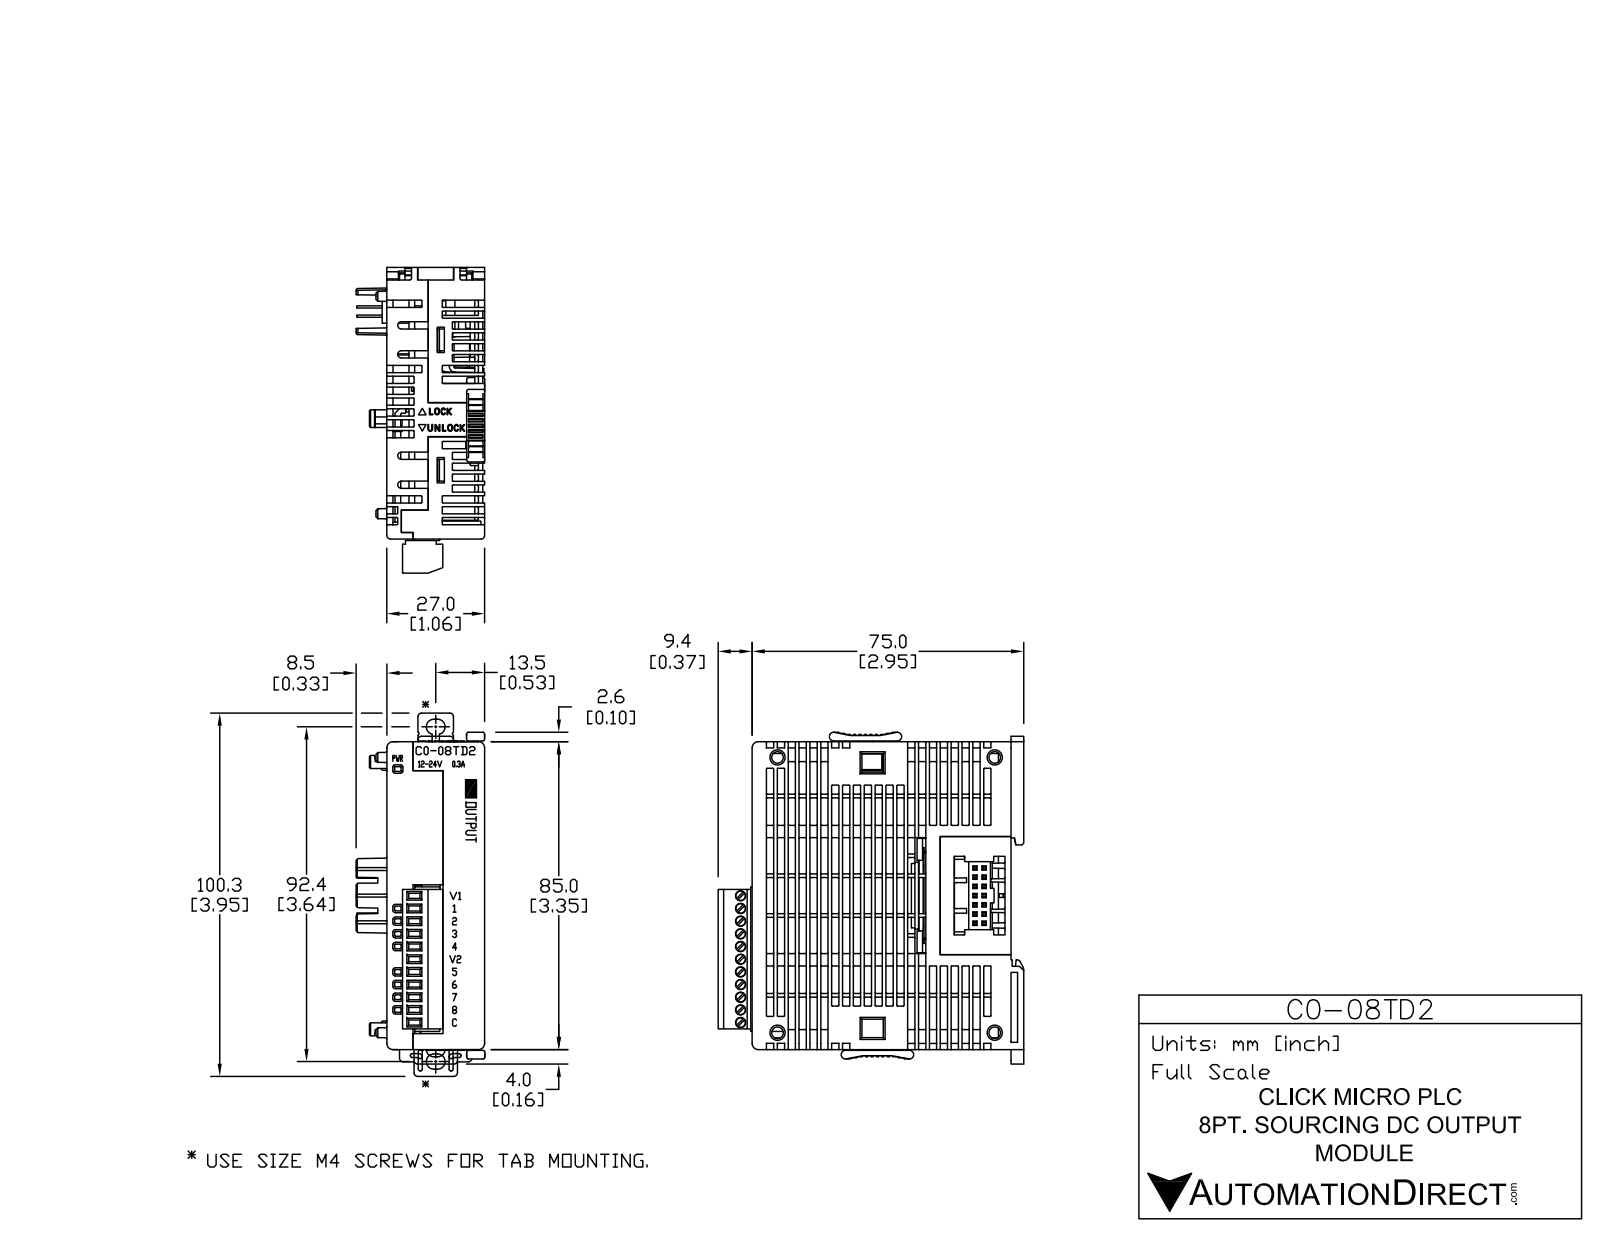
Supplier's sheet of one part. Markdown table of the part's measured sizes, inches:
| quantity | value |
| --- | --- |
| part name | C0-08TD2 |
| STEP written by | SolidWorks 2009 (AUTOMOTIVE_DESIGN) |
| units | inches |
| bodies | 1 solid, 3689 faces (2637 planar, 968 cylindrical, 84 other) |
| overall size | 3.606 × 3.323 × 1.4 |
| volume | 9.917 in³ |
| surface area | 49.24 in² |
| round holes (diameter × count) | 0.039 × 11, 0.11 × 11, 0.126 × 4, 0.079 × 2 |
| round bosses / shafts (diameter × count) | 0.102 × 11, 0.075 × 1 |
| partial cylindrical surfaces (radius × count) | 0.008 × 570, 0.02 × 43, 0.012 × 22, 0.039 × 18, 0.047 × 12, 0.11 × 11, 0.067 × 6, 0.083 × 4 |
| main face-to-face distances | 1.063, 0.02, 0.02, 1.043, 2.815, 0.067, 3.346, 1.035, 1.056, 3.327 |
| hole center spacings | 0.138, 0.276, 0.413, 0.551, 0.689, 0.827, 0.965, 1.102 |
